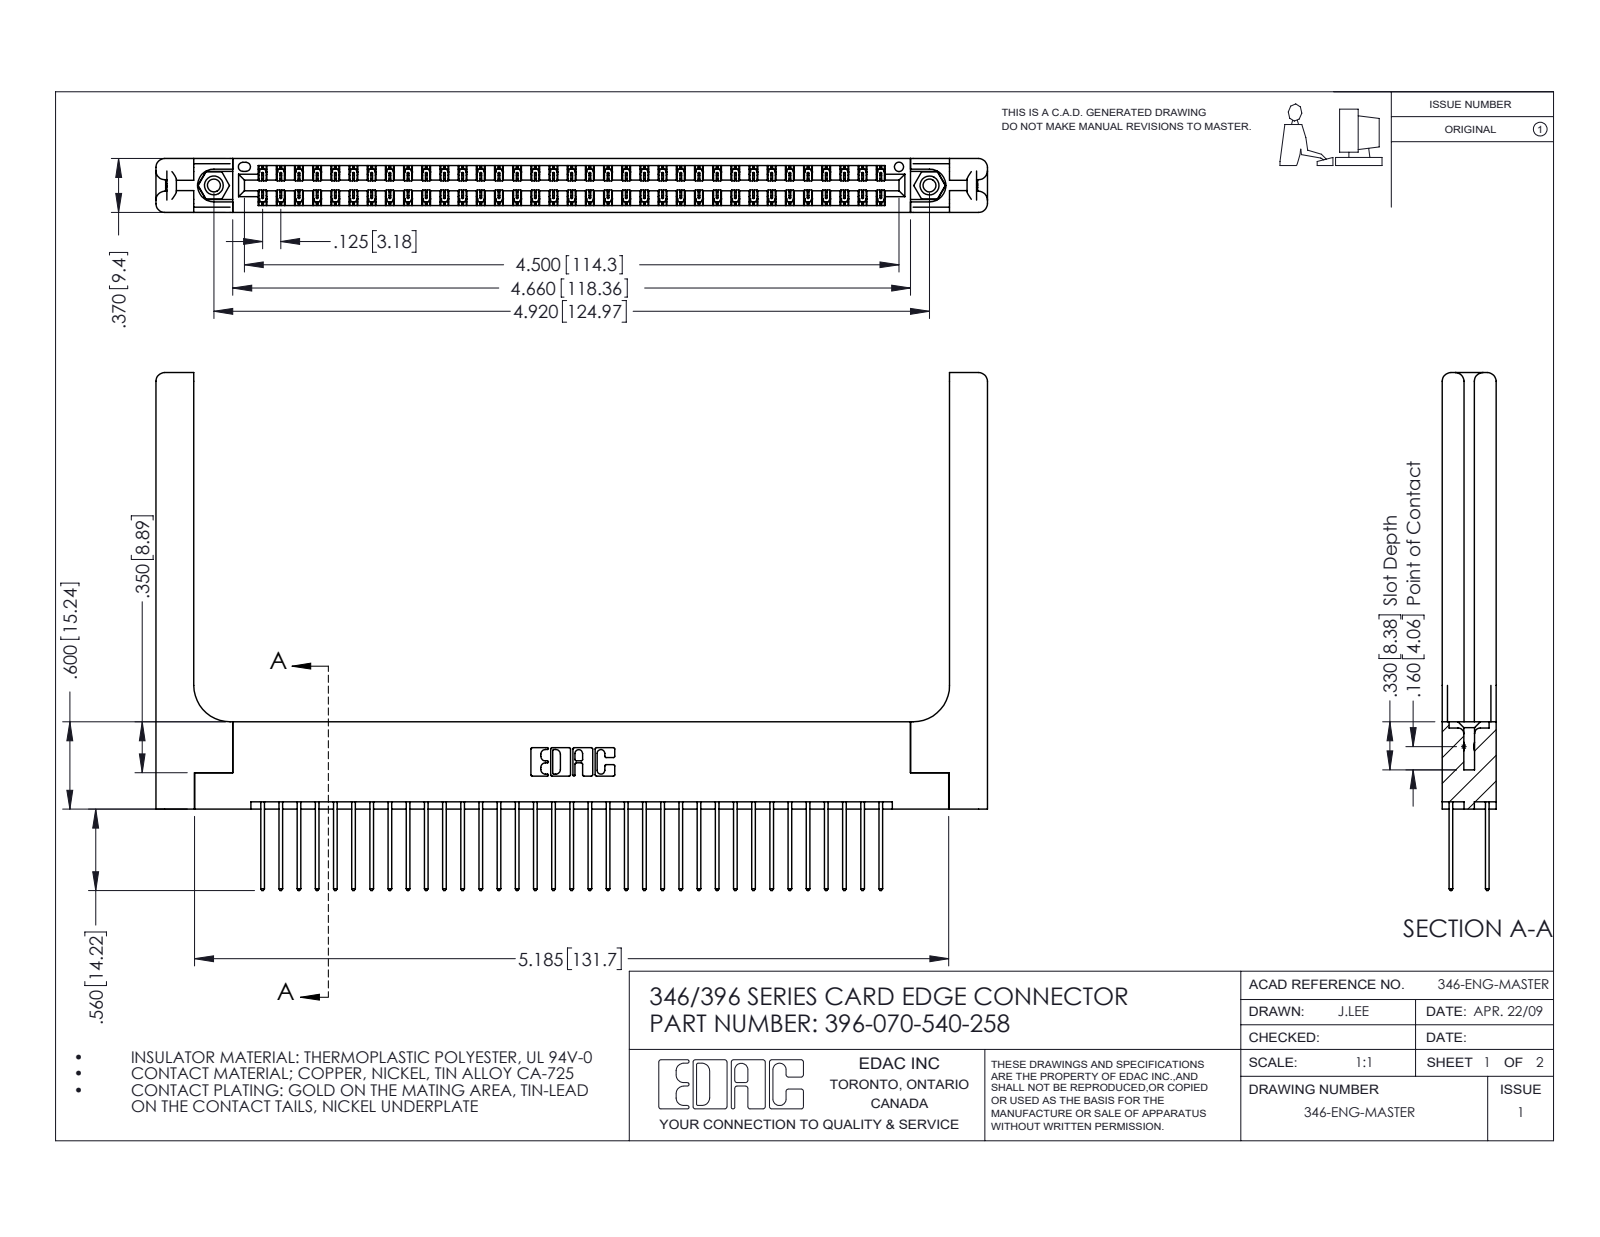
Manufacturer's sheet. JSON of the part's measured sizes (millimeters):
{"part_name": "346 Part_Flush Mounting Lugs - 0.156 Dia-TH; 345-292-001_345-293-140; 346-220-058_345-220-058; 396-070-540-258 (+1 more)", "step_written_by": "SolidWorks 2016 (CONFIG_CONTROL_DESIGN)", "units": "millimeters", "bodies": {"solids": 75, "faces": 4018, "planar": 2674, "cylindrical": 1284, "other": 60}, "overall_size": [145.2, 90.4, 9.4], "volume_mm3": 21860, "surface_area_mm2": 25870, "round_holes": [[2.3, 2], [3.2, 2], [4, 2], [1.6, 1]], "round_bosses_or_shafts": [[3.9, 2]], "partial_cylinders_radius": [[0.2, 105], [0.3, 70], [0.3, 22], [1.5, 16], [0.2, 6], [0.8, 6], [0.7, 3], [0.4, 2]], "face_to_face_distances": [1.2, 8.2, 1.8, 9.4, 6.4, 0.6, 7.6, 3.8, 3.8, 7], "hole_center_spacings": [6.2, 119.7, 125]}
